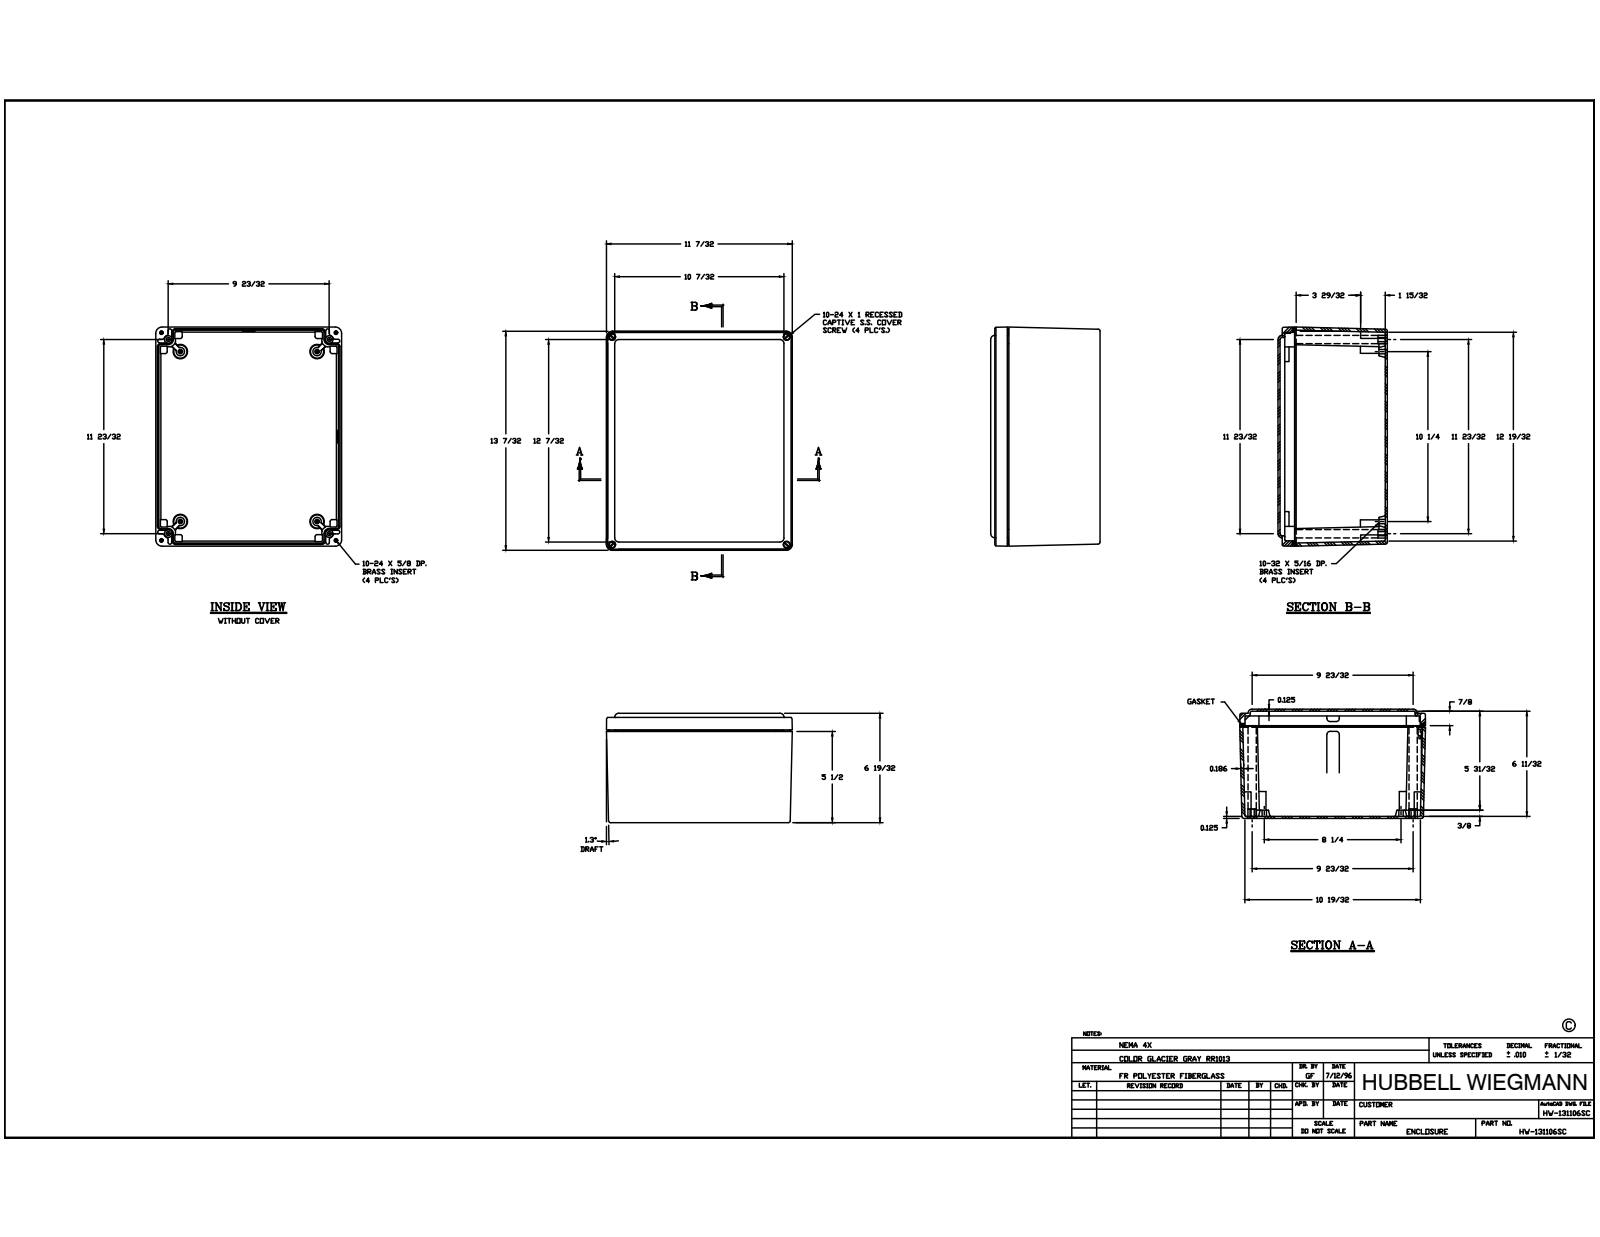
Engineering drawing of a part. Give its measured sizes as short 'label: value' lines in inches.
name: WP1311WBOX; 0.3125-18 X 0.563 DP BRASS INSERT; 10-32 X0.3125 DP BRASS INSERT; 10-24 X 0.625 DP BRASS INSERT (+5 more)
written by: Autodesk Inventor 2014 (AUTOMOTIVE_DESIGN)
unit: in
bodies: 23 solids, 1101 faces (437 planar, 296 cylindrical, 368 other)
size: 13.219 × 11.219 × 6.594
volume: 109.3 in³; area: 1 295 in²
holes: 8× ⌀0.281, 4× ⌀0.145, 4× ⌀0.156, 4× ⌀0.156, 4× ⌀0.19, 4× ⌀0.219, 4× ⌀0.23, 4× ⌀0.28, 4× ⌀0.313, 4× ⌀0.406, 4× ⌀0.531
bosses: 4× ⌀0.375, 4× ⌀0.364, 4× ⌀0.191
rounds: 57× R0.031, 38× R0.125, 29× R0.063, 16× R0.01, 8× R0.059, 8× R0.188, 8× R0.25, 8× R0.375
face distances: 0.186, 0.125, 6.344, 6.594, 6.469, 6.469, 0.125, 0.25, 6.219, 0.75
hole spacings: 0.574, 0.575, 1.039, 1.613, 1.613, 9.014, 9.459, 9.459
